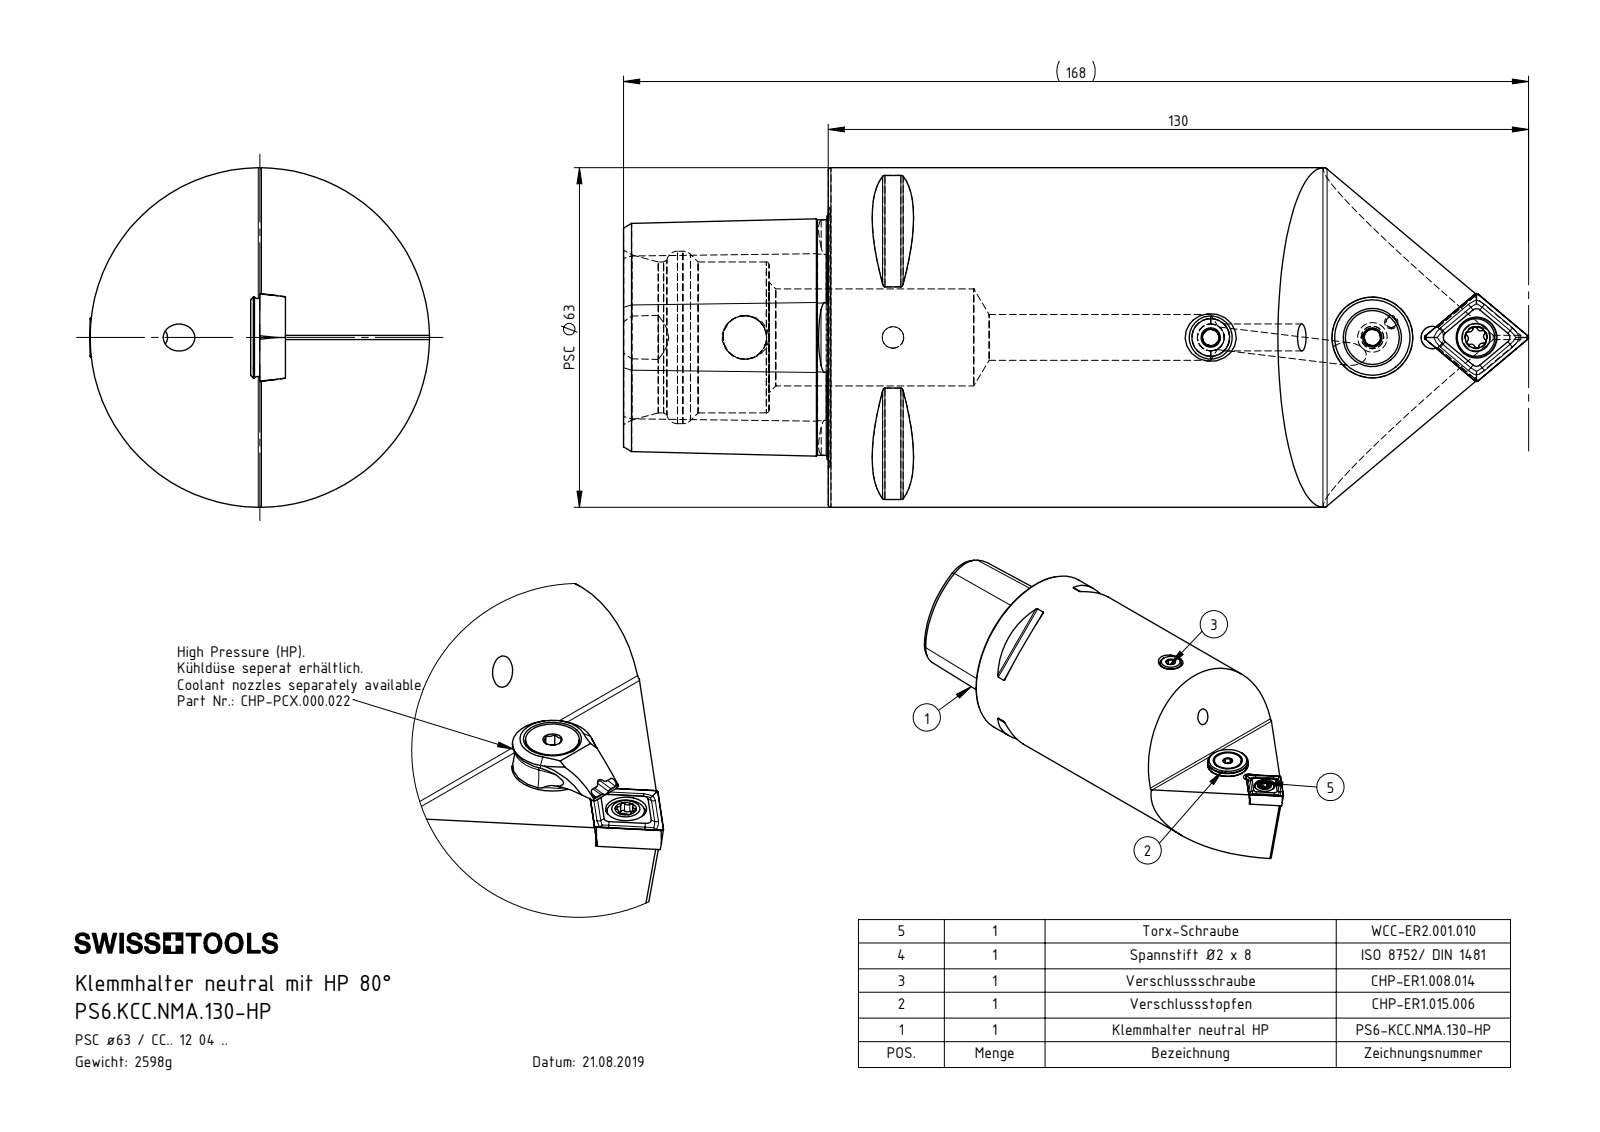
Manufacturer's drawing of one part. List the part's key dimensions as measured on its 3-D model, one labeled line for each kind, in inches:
Part name (STEP PRODUCT): PS6.KCC.NMA.130-HP; CHP-ER1.015.006; WCC-ER2.001.010_A; DIN 3771 - 13x1 (+6 more)
STEP written by: SolidWorks 2017 (AUTOMOTIVE_DESIGN)
Units: inches
Bodies: 8 solids, 370 faces (86 planar, 98 cylindrical, 186 other)
Overall size (bounding box): 6.614 × 2.485 × 2.48
Volume: 20.08 in³ · Surface area: 66.65 in²
Round holes (diameter × count): ⌀0.165 ×4, ⌀0.197 ×2, ⌀0.047 ×1, ⌀0.079 ×1, ⌀0.098 ×1, ⌀0.118 ×1, ⌀0.157 ×1, ⌀0.205 ×1, ⌀0.217 ×1, ⌀0.276 ×1, ⌀0.299 ×1, ⌀0.319 ×1
Round bosses / shafts (diameter × count): ⌀0.197 ×2, ⌀2.48 ×1, ⌀0.591 ×1, ⌀0.528 ×1, ⌀0.394 ×1, ⌀0.315 ×1, ⌀0.276 ×1, ⌀0.217 ×1
Partial cylindrical surfaces — rounded edges, fillets, slot ends (radius × count): R0.02 ×10, R0.015 ×6, R0.027 ×3, R0.027 ×3, R0.236 ×1, R0.276 ×1
Main face-to-face distances: 3.346, 1.496, 4.843, 0.98, 0.177, 1.063, 0.433, 3.78, 0.176, 2.197
Hole centre spacings: 0.177, 0.319, 0.323, 0.348, 0.482, 0.666, 0.67, 0.798
